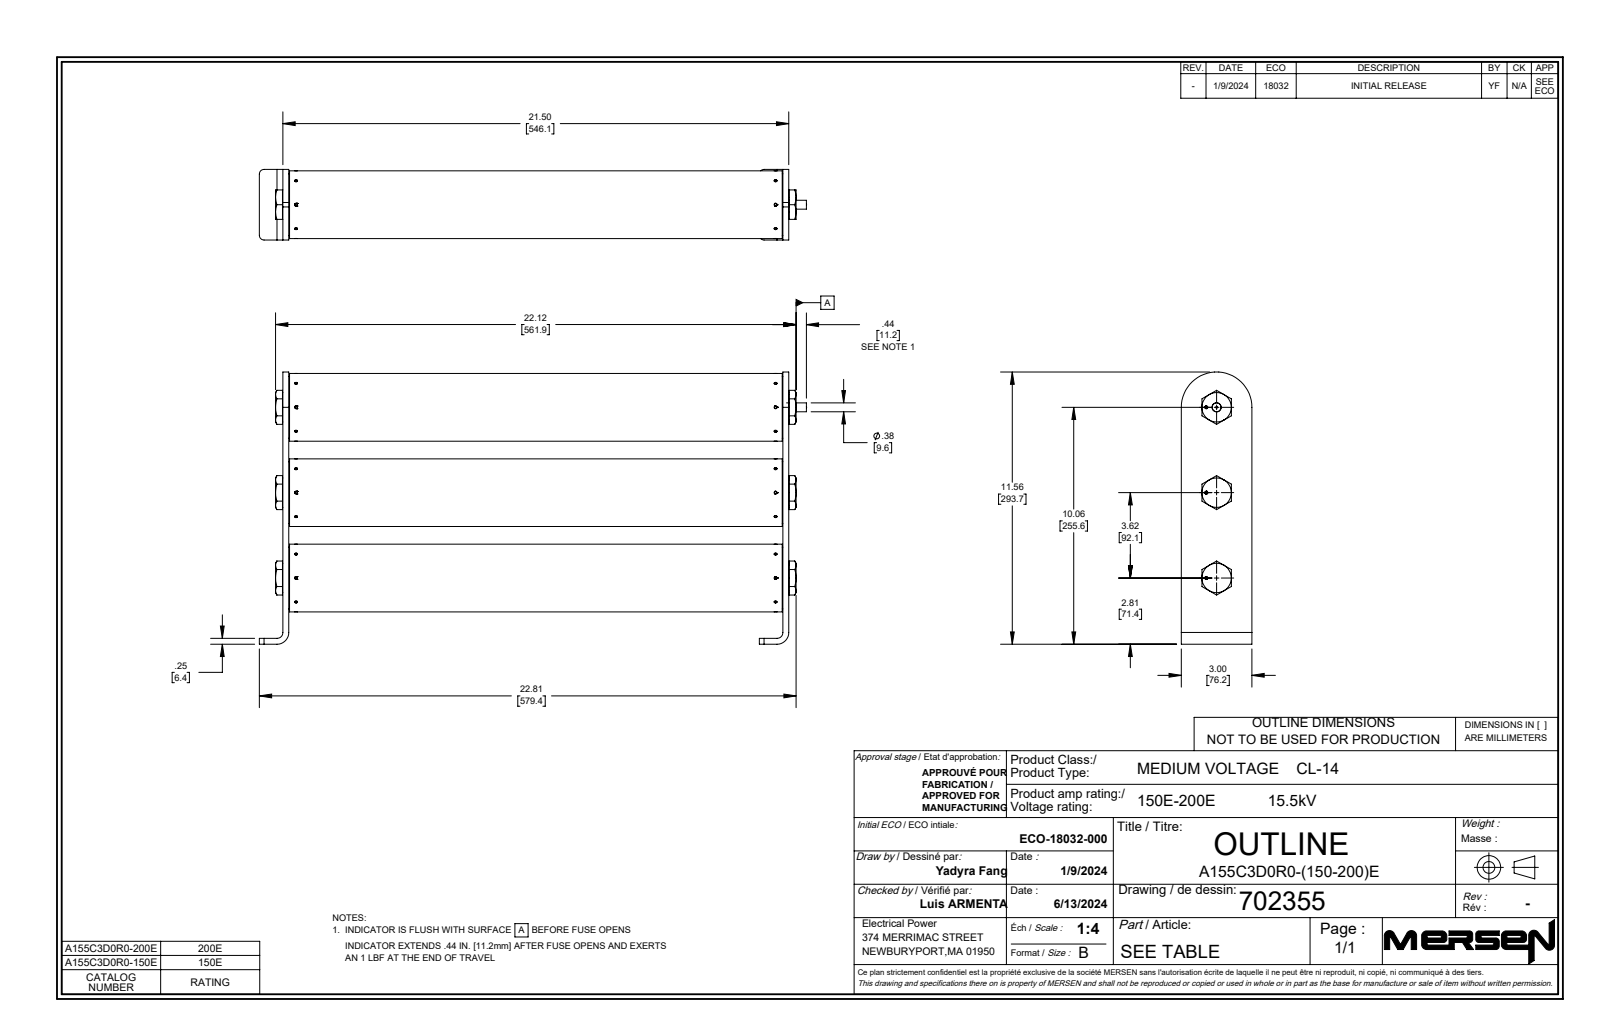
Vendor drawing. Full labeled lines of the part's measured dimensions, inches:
Part name (STEP PRODUCT): 210008_-001; 11378_CRIMPED; 702355; 35980_35980 (+8 more)
STEP written by: SolidWorks 2021 (AUTOMOTIVE_DESIGN)
Units: inches
Bodies: 70 solids, 5634 faces (1400 planar, 2412 cylindrical, 1822 other)
Overall size (bounding box): 22.812 × 11.56 × 3
Volume: 90.68 in³ · Surface area: 1 309 in²
Round holes (diameter × count): ⌀0.125 ×34, ⌀0.127 ×6, ⌀0.906 ×3, ⌀2.625 ×3, ⌀0.205 ×2, ⌀0.02 ×1, ⌀0.052 ×1, ⌀0.063 ×1, ⌀0.14 ×1, ⌀0.189 ×1, ⌀0.391 ×1, ⌀0.465 ×1
Round bosses / shafts (diameter × count): ⌀0.125 ×34, ⌀2.875 ×3, ⌀1.25 ×3, ⌀0.875 ×3, ⌀0.782 ×3, ⌀0.255 ×2, ⌀0.875 ×1, ⌀0.78 ×1
Partial cylindrical surfaces — rounded edges, fillets, slot ends (radius × count): R4 ×161, R0.025 ×6, R0.033 ×6, R0.041 ×6, R0.041 ×6, R0.049 ×6, R0.05 ×6, R0.057 ×6
Main face-to-face distances: 0.25, 21.25, 21.5, 21, 0.312, 21.562, 0.562, 21.812, 0.593, 21.531
Hole centre spacings: 20.541, 20.38, 2.563, 2.563, 5.126, 21.015, 0.438, 3.625
